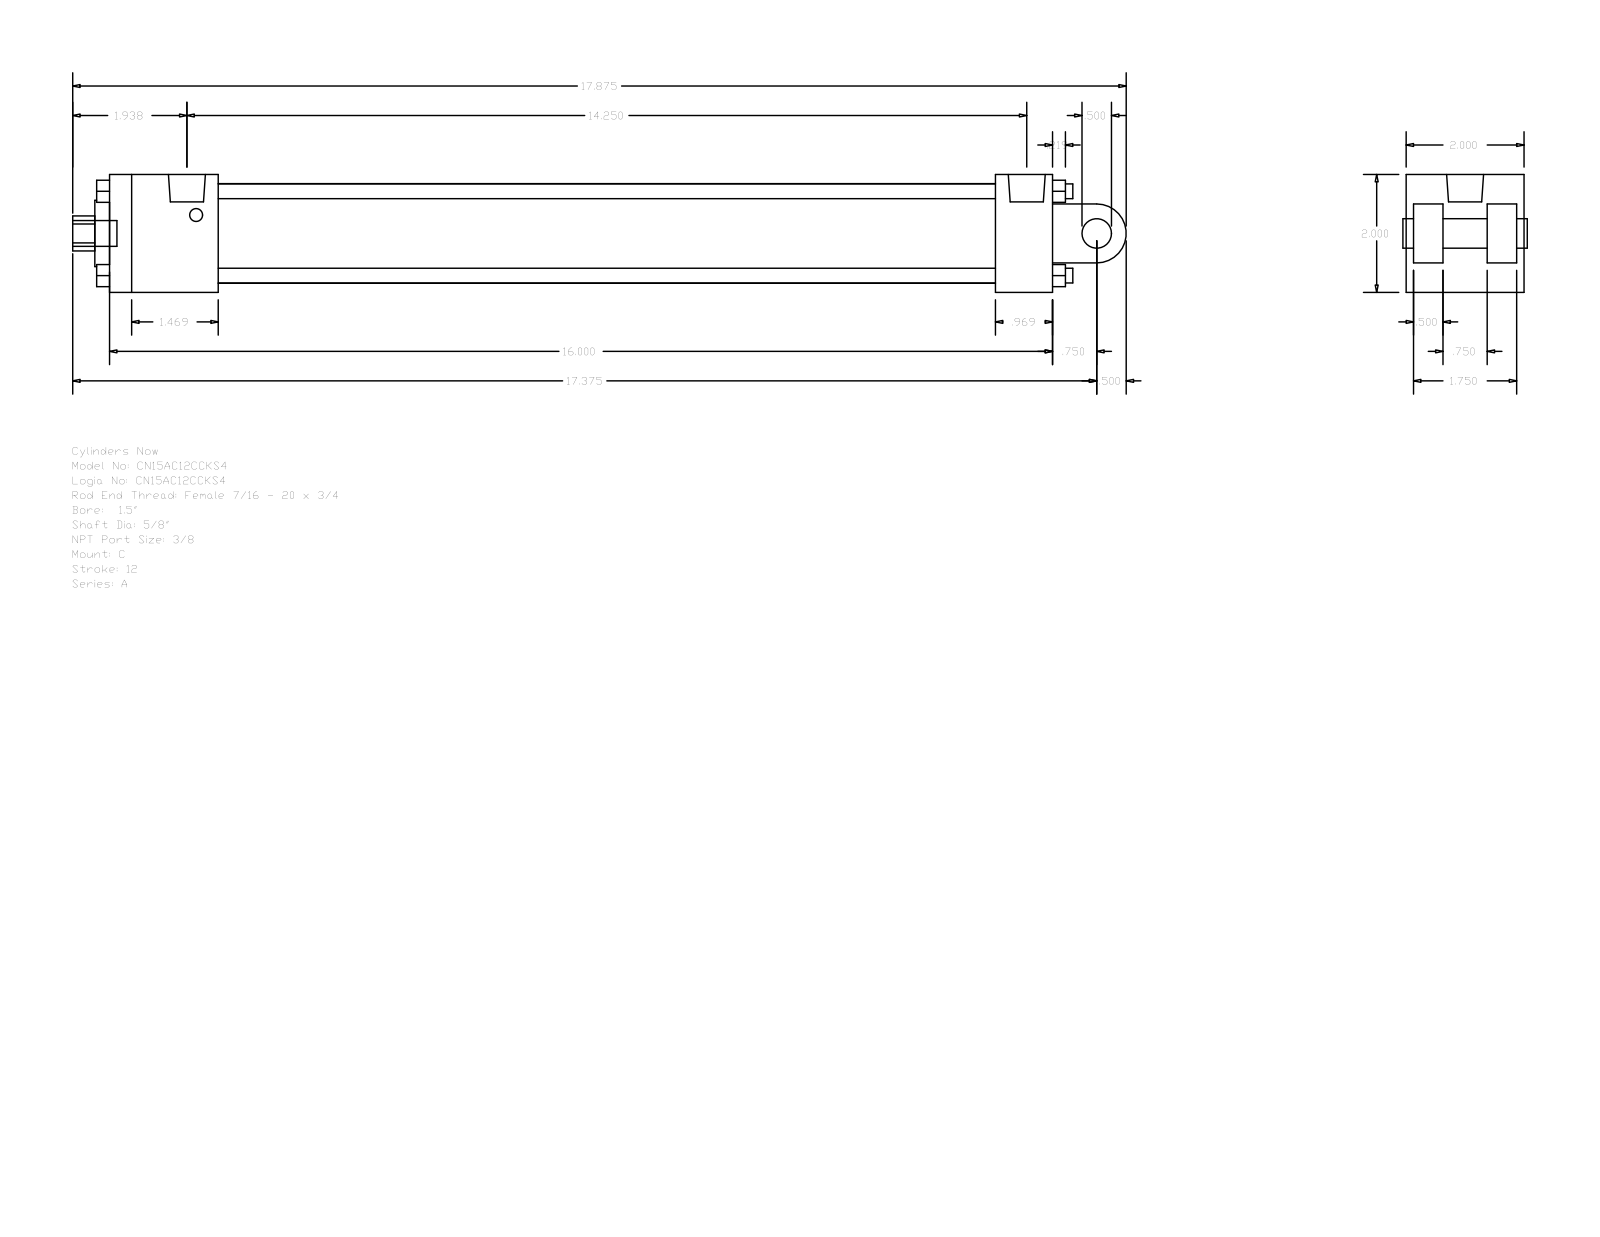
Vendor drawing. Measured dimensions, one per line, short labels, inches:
name: A_C__0150_0.625
written by: GSSL Pune (CONFIG_CONTROL_DESIGN)
unit: in
bodies: 0 solids, 135 faces (102 planar, 33 cylindrical, 0 other)
size: 17.875 × 2 × 2
holes: 2× ⌀0.219, 1× ⌀0.625, 1× ⌀0.627, 1× ⌀1.125, 1× ⌀1.69
bosses: 4× ⌀0.25, 2× ⌀0.219, 1× ⌀0.627, 1× ⌀0.5, 1× ⌀0.437
rounds: 1× R0.297, 1× R0.5
face distances: 2, 0.5, 16, 0.125, 0.625, 1.375, 1.875, 1.25, 15.031, 0.969
hole spacings: 0.156
